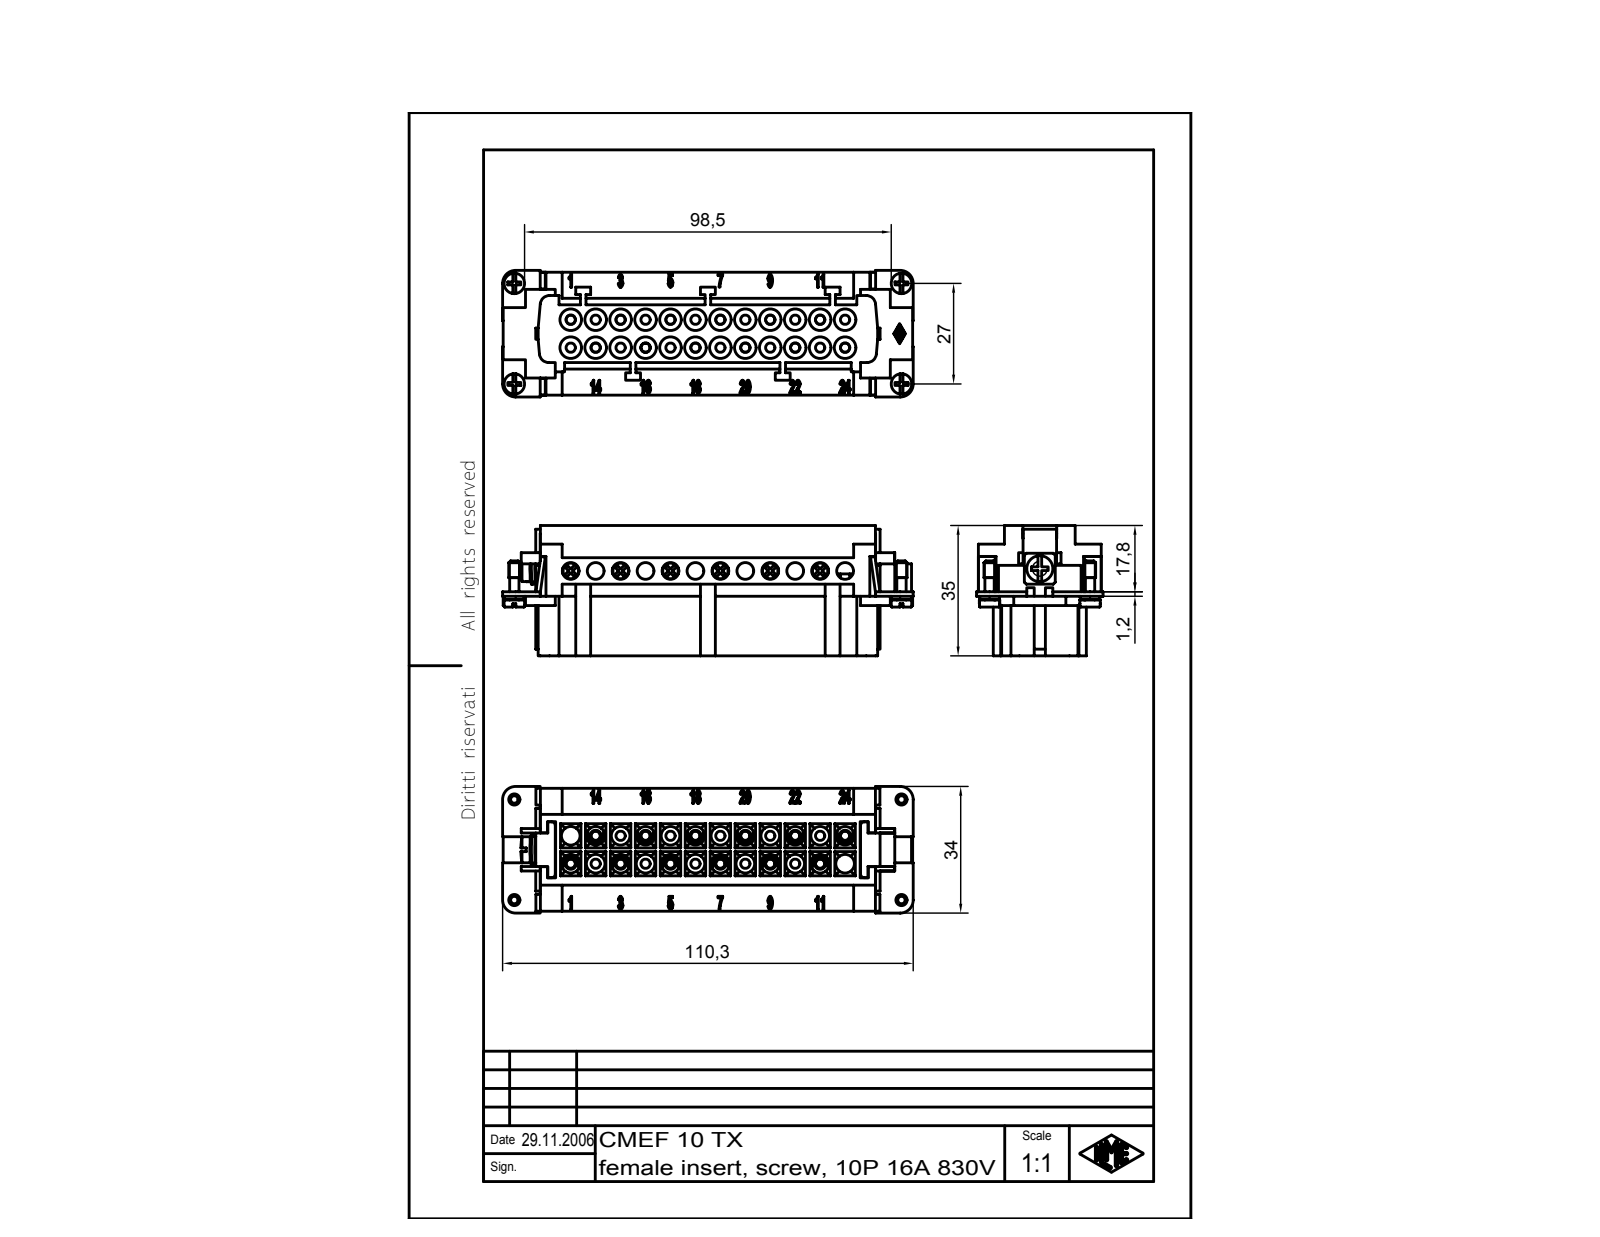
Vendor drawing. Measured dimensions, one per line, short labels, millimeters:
name: CMEF 10 TX
written by: Autodesk Inventor 7 (AUTOMOTIVE_DESIGN)
unit: mm
bodies: 25 solids, 1908 faces (926 planar, 286 cylindrical, 696 other)
size: 110.3 × 35 × 34
volume: 53 419 mm³; area: 40 324 mm²
holes: 12× ⌀3, 12× ⌀4.5, 11× ⌀5, 2× ⌀2.55
bosses: 16× ⌀2.5, 12× ⌀4.2, 2× ⌀5.5, 2× ⌀5.3, 2× ⌀5, 2× ⌀3, 1× ⌀7
rounds: 14× R0.1, 12× R2.1, 4× R2.5, 2× R1, 2× R3.5, 1× R1.62, 1× R5.5
face distances: 1.75, 17.25, 19, 16, 15.5, 8.75, 7, 3.25, 7.1, 24.25
hole spacings: 13.4, 6.7, 26.8, 20.1, 40.2, 33.5, 10.06, 15.36
